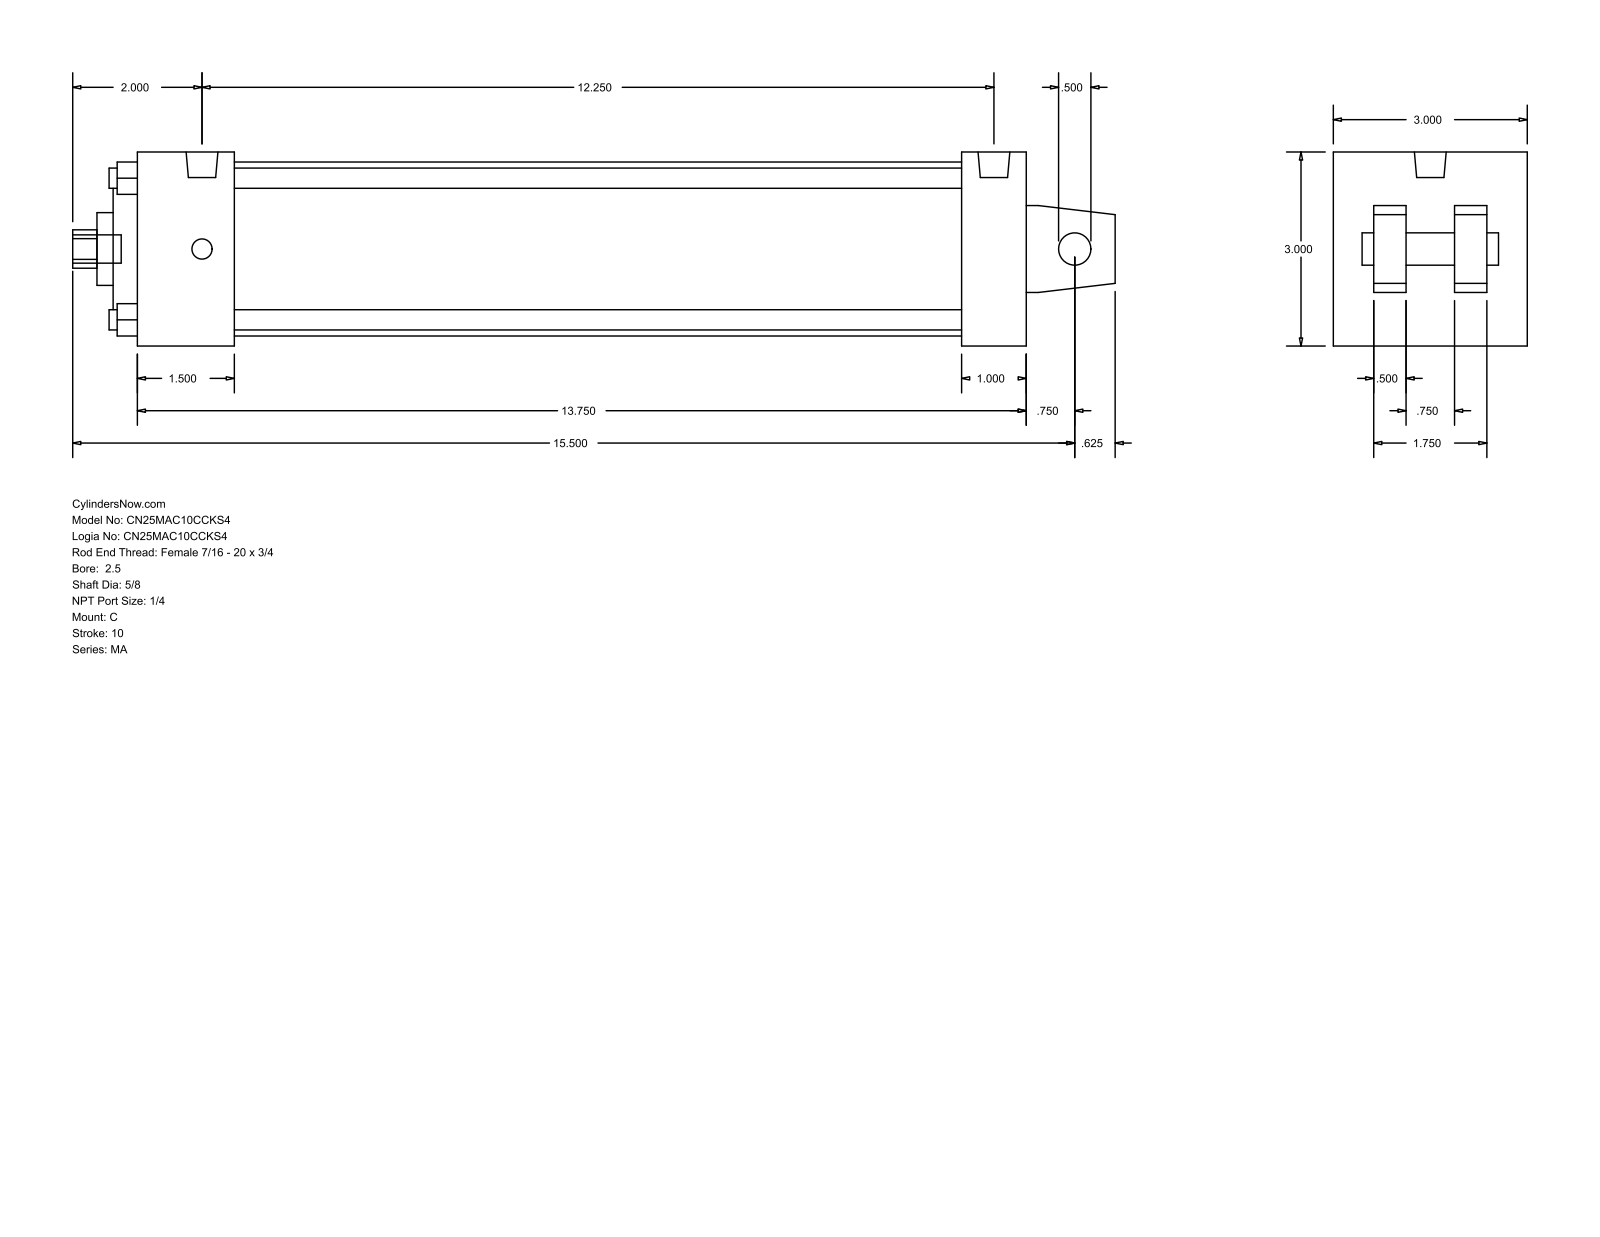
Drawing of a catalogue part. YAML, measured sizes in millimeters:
part_name: "MA_C__0250_0.625"
step_written_by: "GSSL Pune (CONFIG_CONTROL_DESIGN)"
units: millimeters
bodies: {solids: 0, faces: 105, planar: 77, cylindrical: 28, other: 0}
overall_size: [409.57, 76.2, 76.2]
round_holes:
  - {diameter: 7.94, count: 4}
  - {diameter: 12.7, count: 1}
  - {diameter: 15.88, count: 1}
  - {diameter: 28.57, count: 1}
  - {diameter: 50.8, count: 1}
  - {diameter: 68.33, count: 1}
round_bosses_or_shafts:
  - {diameter: 7.94, count: 4}
  - {diameter: 12.49, count: 2}
  - {diameter: 11.11, count: 1}
partial_cylinders:
  - {radius: 7.54, count: 1}
face_to_face_distances: [76.2, 349.25, 12.7, 15.87, 47.63, 25.4, 38.1, 323.85, 285.75, 311.15]
hole_center_spacings: [39.33, 55.62, 78.66]
